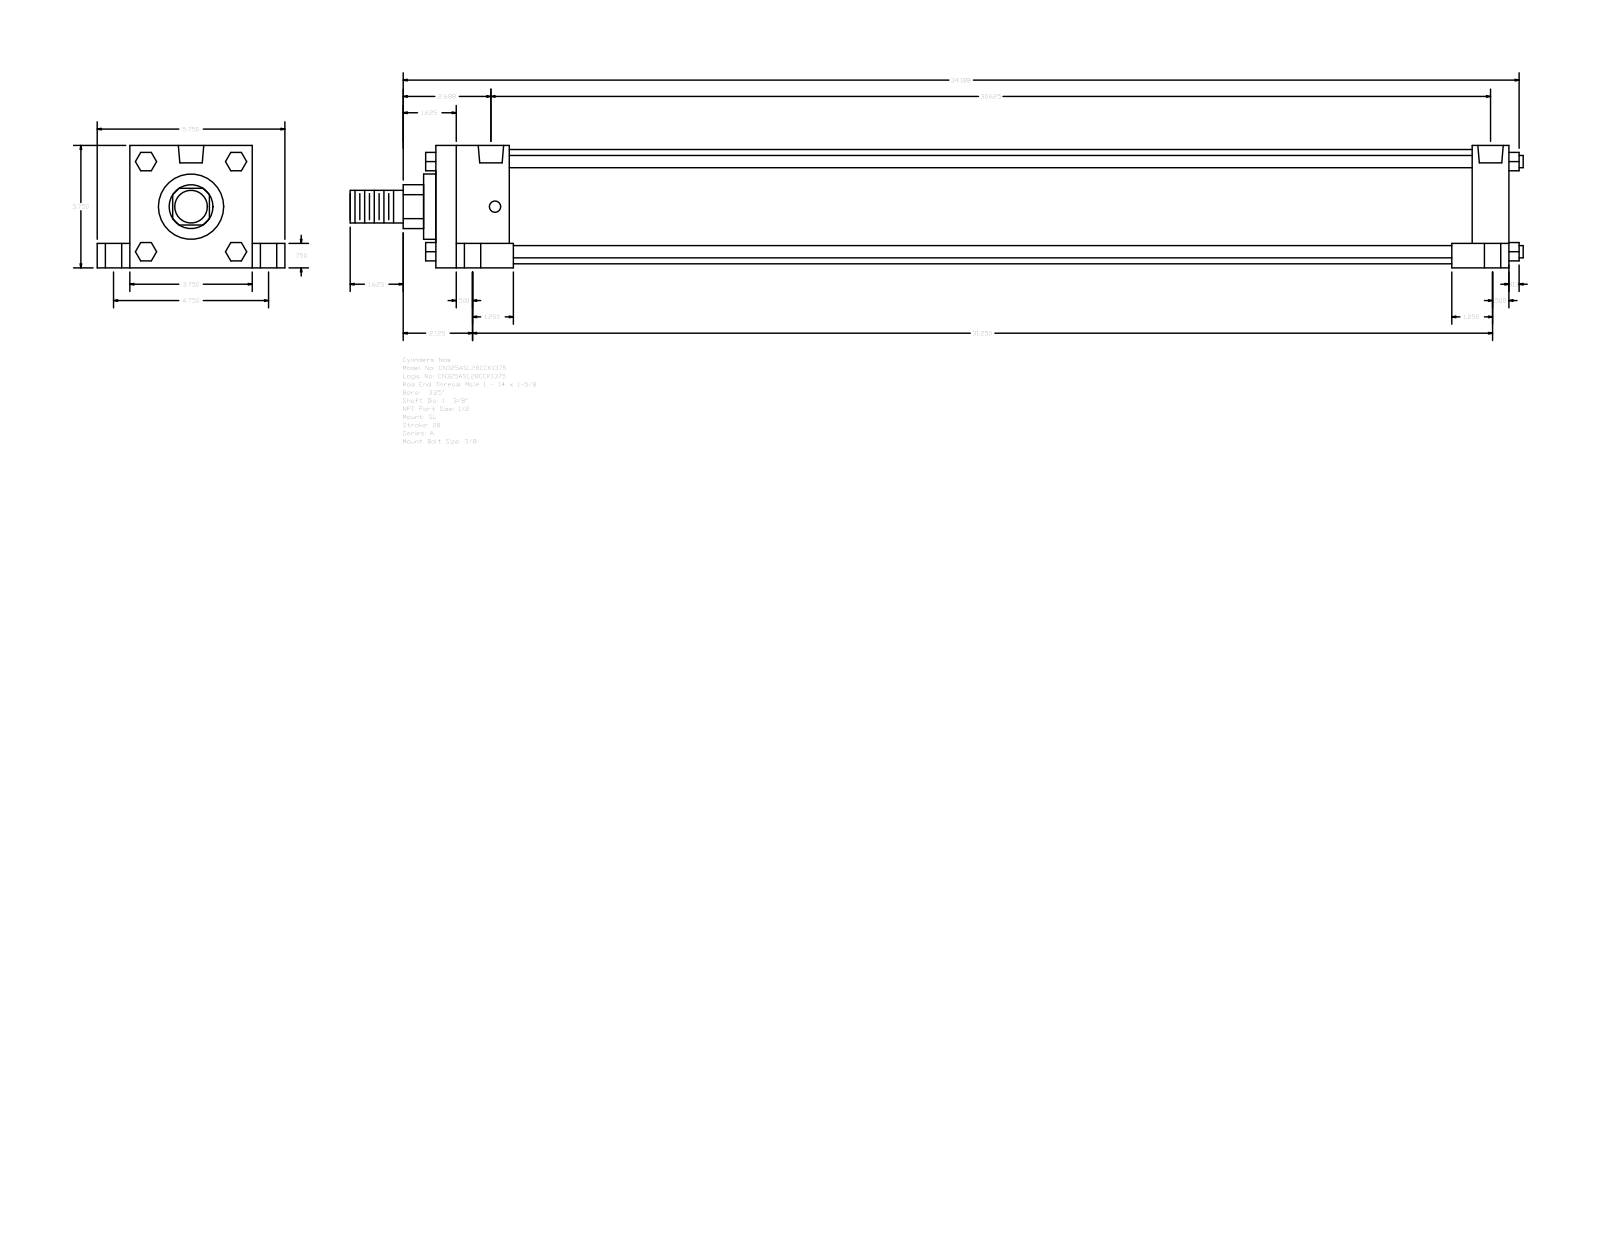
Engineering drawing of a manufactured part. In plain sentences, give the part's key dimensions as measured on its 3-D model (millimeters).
The part is named "A_SL__0325_1.375". Its 3-D file was written by "GSSL Pune (CONFIG_CONTROL_DESIGN)". It is 0 solids with 150 faces: 114 planar, 36 cylindrical and 0 other. Overall it measures 912.81 by 146.05 by 95.25 millimeters. Round holes: 4 of diameter 8.73, 4 of diameter 12.7, 4 of diameter 19.05, 2 of diameter 19.77. Round bosses or shafts: 4 of diameter 9.53, 1 of diameter 88.9, 1 of diameter 50.8, 1 of diameter 34.92, 1 of diameter 25.4. Partial cylindrical surfaces (rounded edges, fillets, slot ends): 1 of radius 17.06. The main face-to-face distances are 95.24, 835.02, 25.41, 120.65, 19.05, 76.19, 57.15, 28.57, 806.45, 749.3. The hole center spacings are 3.18, 60.35, 60.52, 62, 62.81, 120.66, 771.52, 774.7.
